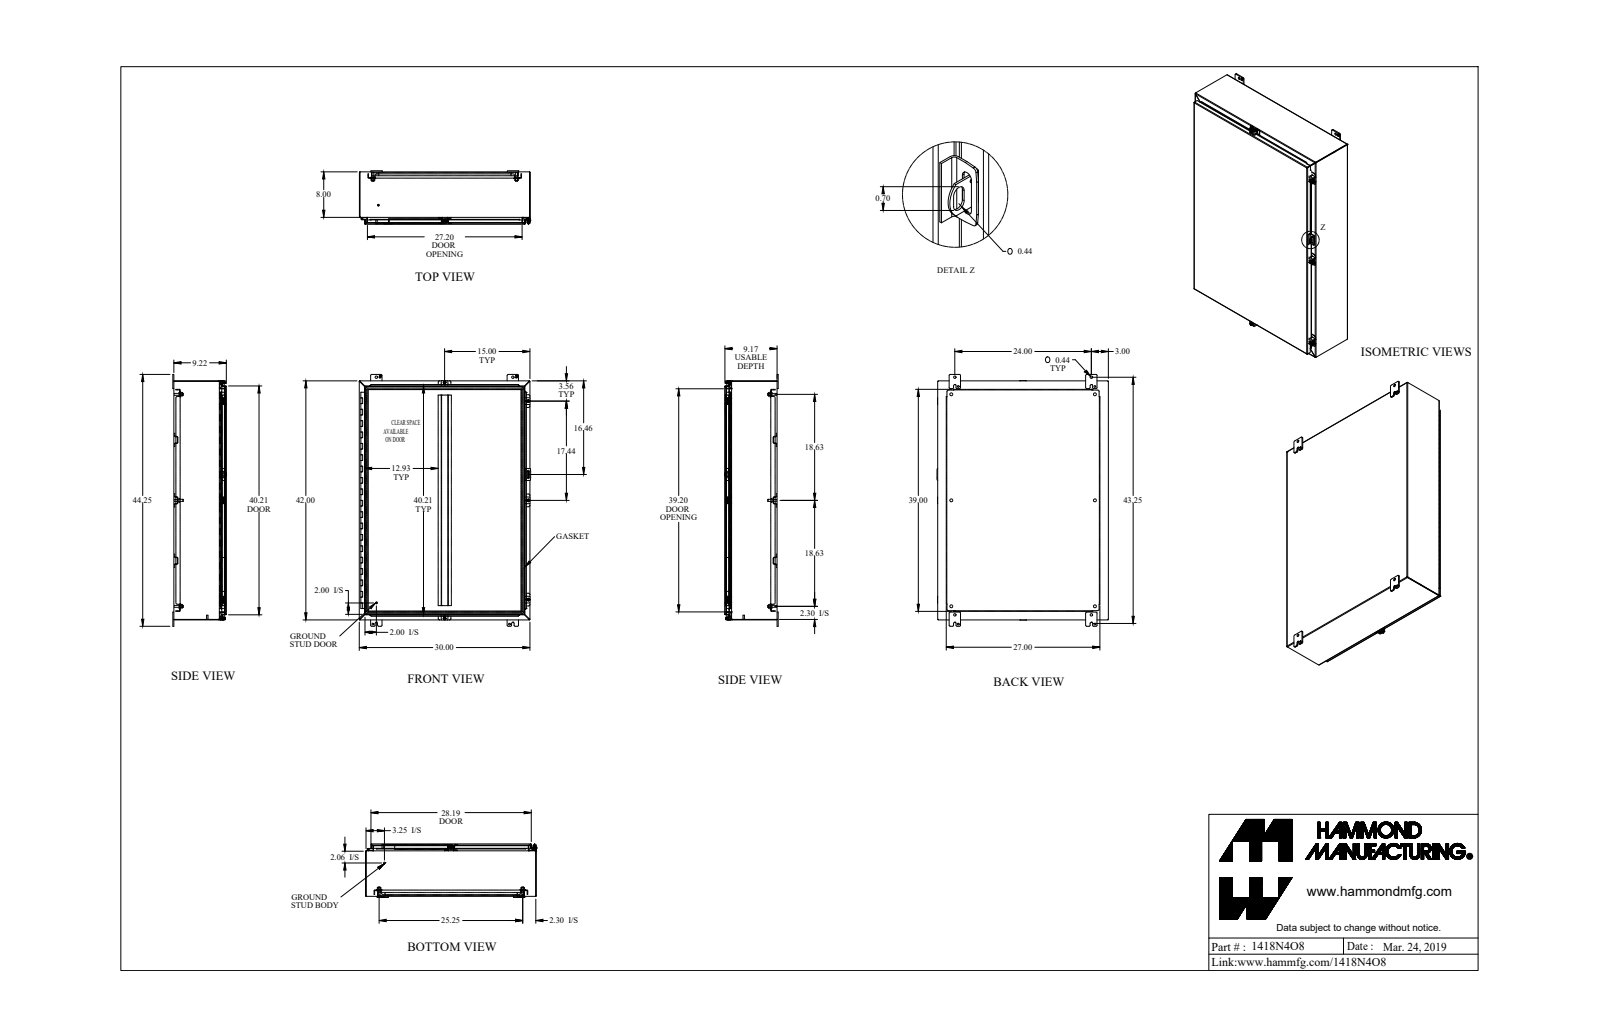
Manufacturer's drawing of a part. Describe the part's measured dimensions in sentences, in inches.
The part is named "1418N4O8_Default". Its 3-D file was written by "SolidWorks 2019 (CONFIG_CONTROL_DESIGN)". It is 53 solids with 1915 faces: 1109 planar, 695 cylindrical and 111 other. Overall it measures 44.25 by 30.126 by 9.437 inches. Its volume is 445.4 cubic inches and its surface area 11 627 square inches. Round holes: 6 of diameter 0.5, 5 of diameter 0.213, 5 of diameter 0.375, 4 of diameter 0.265, 4 of diameter 0.307, 4 of diameter 0.313, 4 of diameter 0.437, 2 of diameter 0.445, 2 of diameter 0.445, 1 of diameter 0.125, 1 of diameter 0.187, 1 of diameter 0.265. Round bosses or shafts: 6 of diameter 0.65, 6 of diameter 0.375, 6 of diameter 0.33, 5 of diameter 0.5, 5 of diameter 0.39, 5 of diameter 0.244, 4 of diameter 1, 2 of diameter 0.281. Partial cylindrical surfaces (rounded edges, fillets, slot ends): 42 of radius 0.188, 36 of radius 0.25, 27 of radius 0.048, 27 of radius 0.143, 24 of radius 0.036, 24 of radius 0.108, 16 of radius 0.116, 12 of radius 0.125. The main face-to-face distances are 0.072, 0.072, 9.071, 9.143, 9.143, 9.215, 8.111, 8.039, 1.032, 1.104. The hole center spacings are 18.625, 41.349, 25.25, 12.802, 12.803, 24, 24.289, 31.376.
